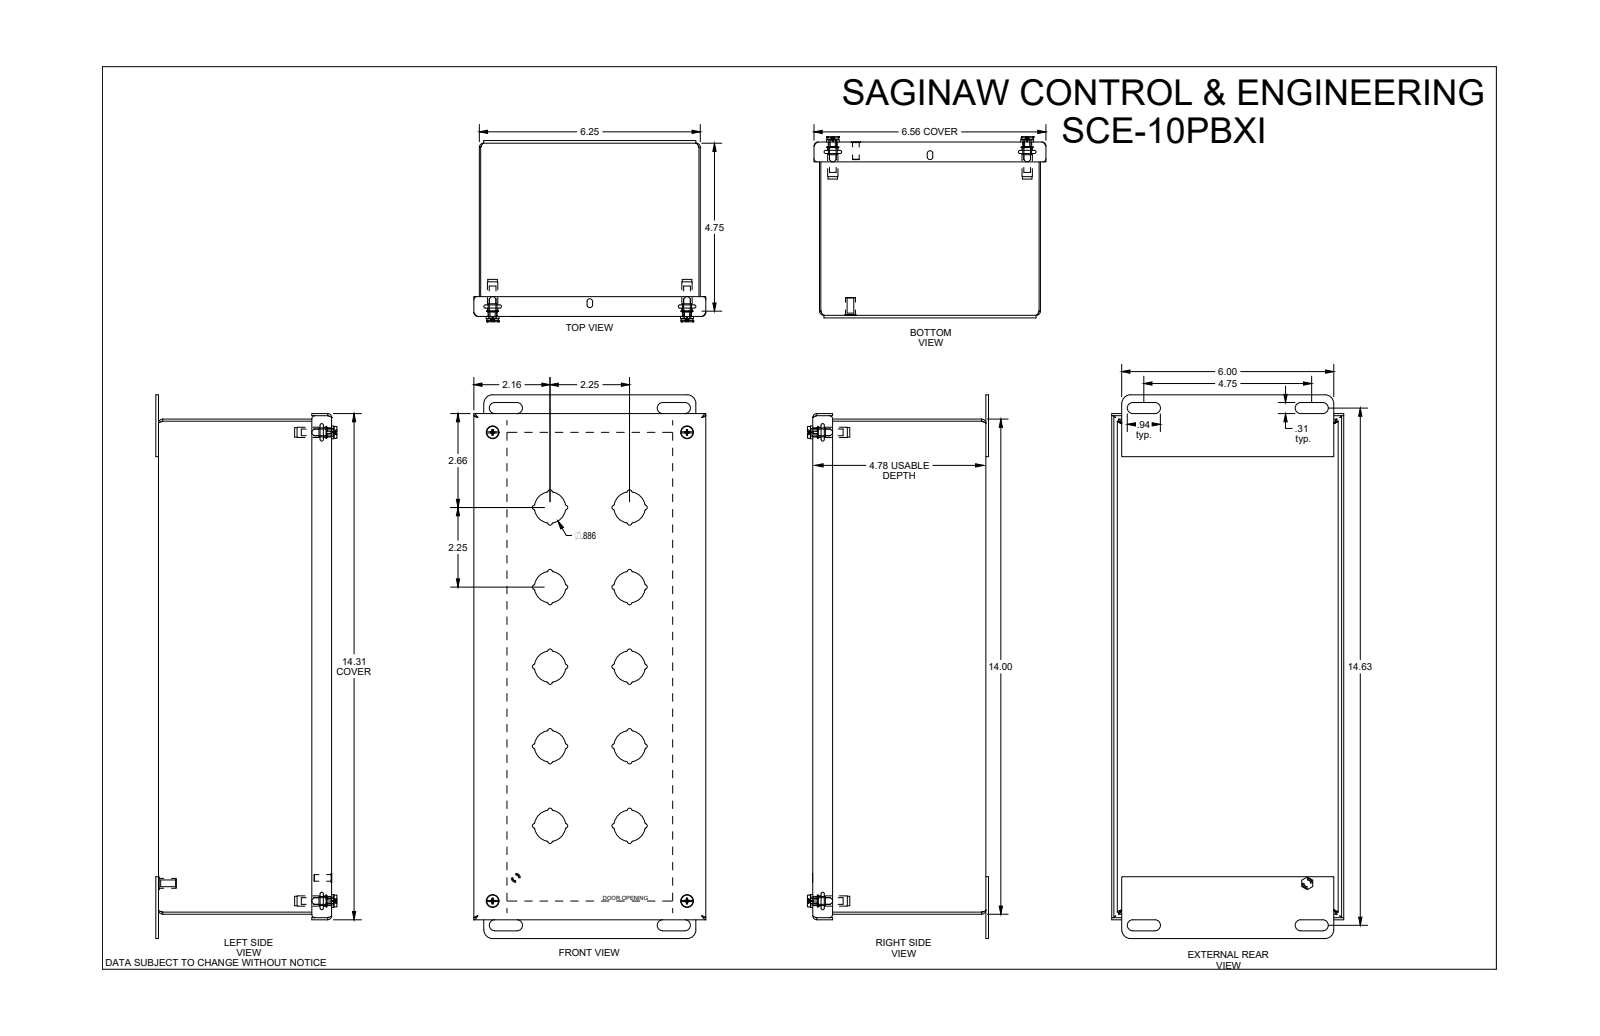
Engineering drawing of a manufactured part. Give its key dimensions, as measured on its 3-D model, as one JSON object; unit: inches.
{"part_name": "SCE-10PBXI", "step_written_by": "SolidWorks 2019 (AUTOMOTIVE_DESIGN)", "units": "inches", "bodies": {"solids": 15, "faces": 580, "planar": 166, "cylindrical": 338, "other": 76}, "overall_size": [15.375, 6.563, 5.036], "volume_in3": 26.92, "surface_area_in2": 894.3, "round_holes": [[0.19, 5], [0.22, 4], [0.25, 4], [0.266, 4], [0.317, 4], [0.193, 1], [0.281, 1]], "round_bosses_or_shafts": [[0.437, 4], [0.362, 4], [0.34, 4], [0.292, 4], [0.27, 4], [0.26, 4], [0.28, 1], [0.256, 1]], "partial_cylinders_radius": [[0.04, 80], [0.062, 40], [0.06, 20], [0.443, 10], [0.015, 8], [0.115, 8], [0.156, 8], [0.245, 8]], "face_to_face_distances": [0.06, 4.838, 6.19, 4.778, 4.898, 6.25, 6.13, 13.94, 4.69, 0.148], "hole_center_spacings": [5.5, 13.25, 14.346, 5.5, 5.025, 13.25, 13.25, 13.695]}
